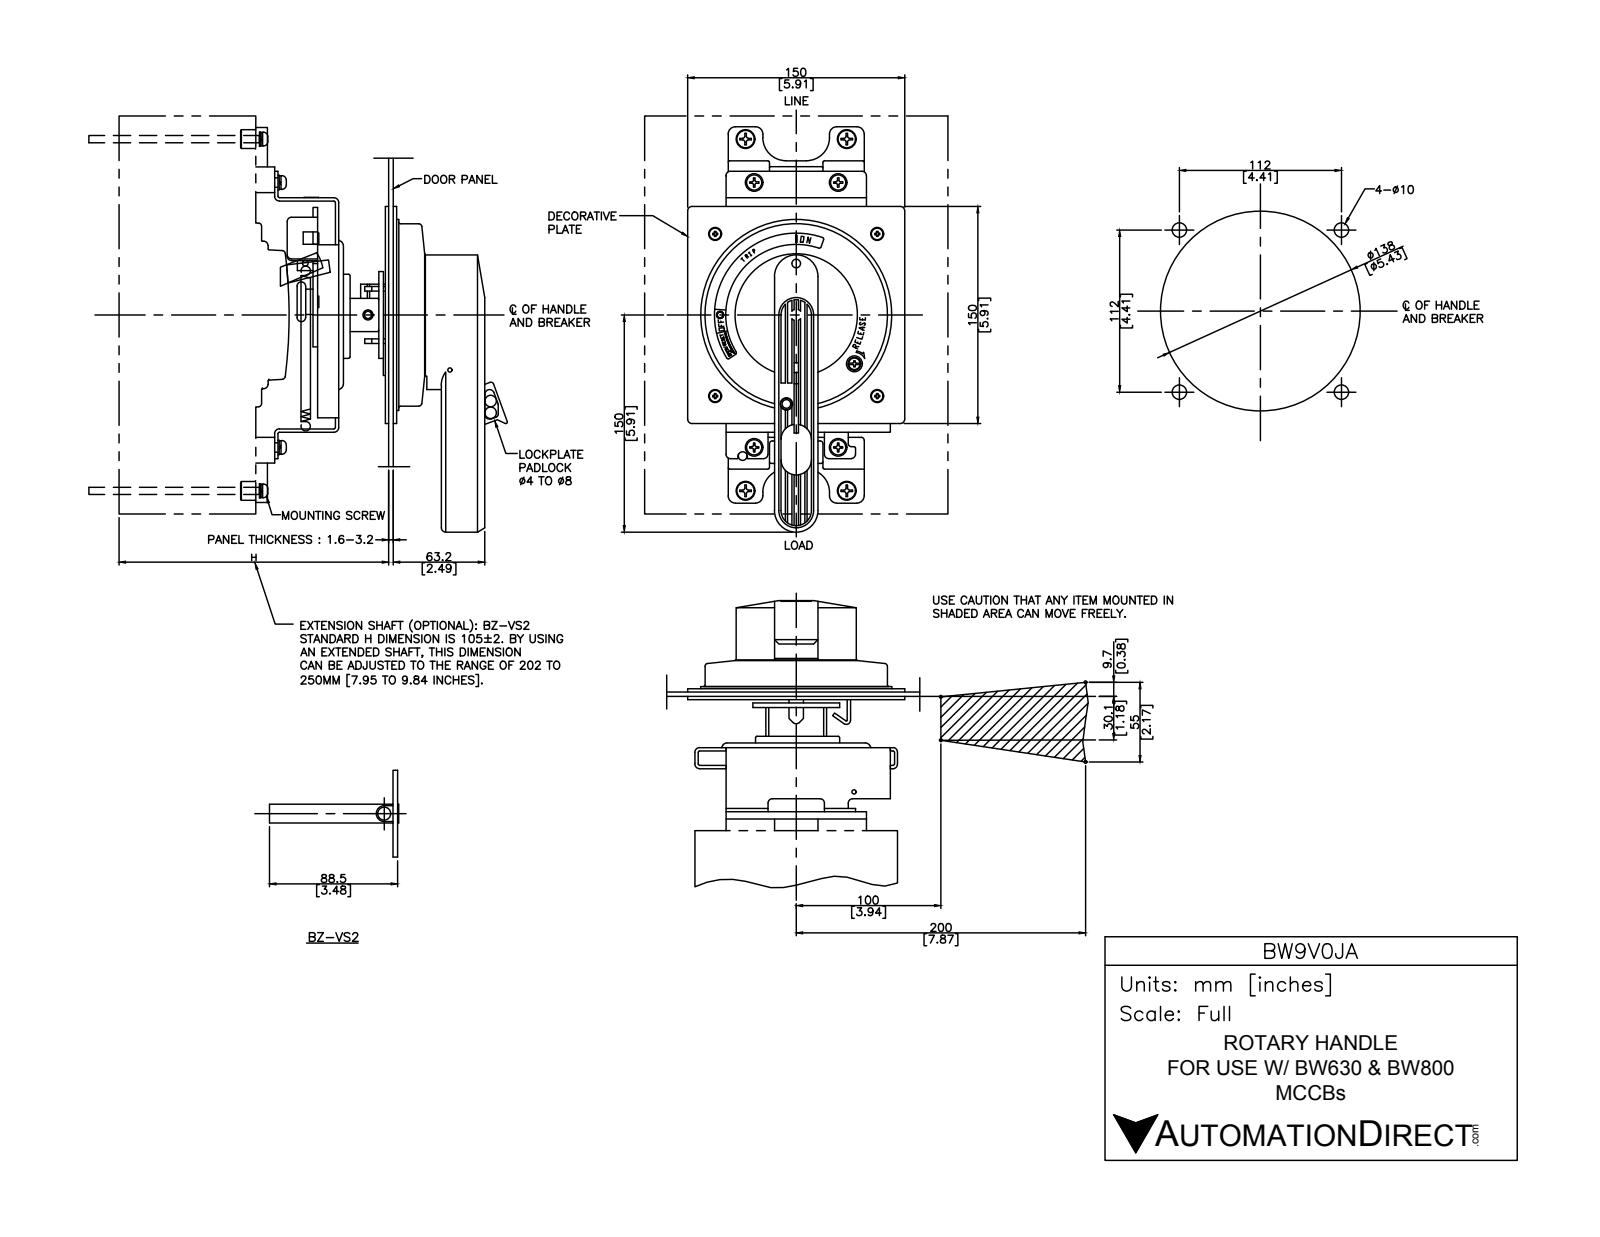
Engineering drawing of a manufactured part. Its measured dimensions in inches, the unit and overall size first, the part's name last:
Units: inches
Overall size (bounding box): 10.453 × 10.394 × 5.906
Round holes (diameter × count): ⌀0.256 ×8, ⌀0.157 ×4, ⌀0.315 ×4, ⌀0.512 ×4, ⌀0.197 ×1, ⌀1.496 ×1, ⌀3.327 ×1
Round bosses / shafts (diameter × count): ⌀0.413 ×4, ⌀0.276 ×4, ⌀0.236 ×4, ⌀5.118 ×1, ⌀4.961 ×1, ⌀4.134 ×1, ⌀3.307 ×1, ⌀2.992 ×1
Partial cylindrical surfaces — rounded edges, fillets, slot ends (radius × count): R0.079 ×27, R0.118 ×19, R0.197 ×8, R0.295 ×7, R0.059 ×6, R0.039 ×4, R0.13 ×4, R0.512 ×4
Main face-to-face distances: 0.091, 1.181, 1.48, 1.39, 0.965, 0.299, 0.209, 1.173, 1.965, 1.091
Hole centre spacings: 0.687, 1.756, 2.104, 2.43, 3.118, 3.627, 3.68, 3.779
Volume: 44.05 in³ · Surface area: 380.8 in²
Bodies: 17 solids, 469 faces (215 planar, 238 cylindrical, 16 other)
Part name (STEP PRODUCT): BW9V0JA
STEP written by: SolidWorks 2018 (AUTOMOTIVE_DESIGN)
